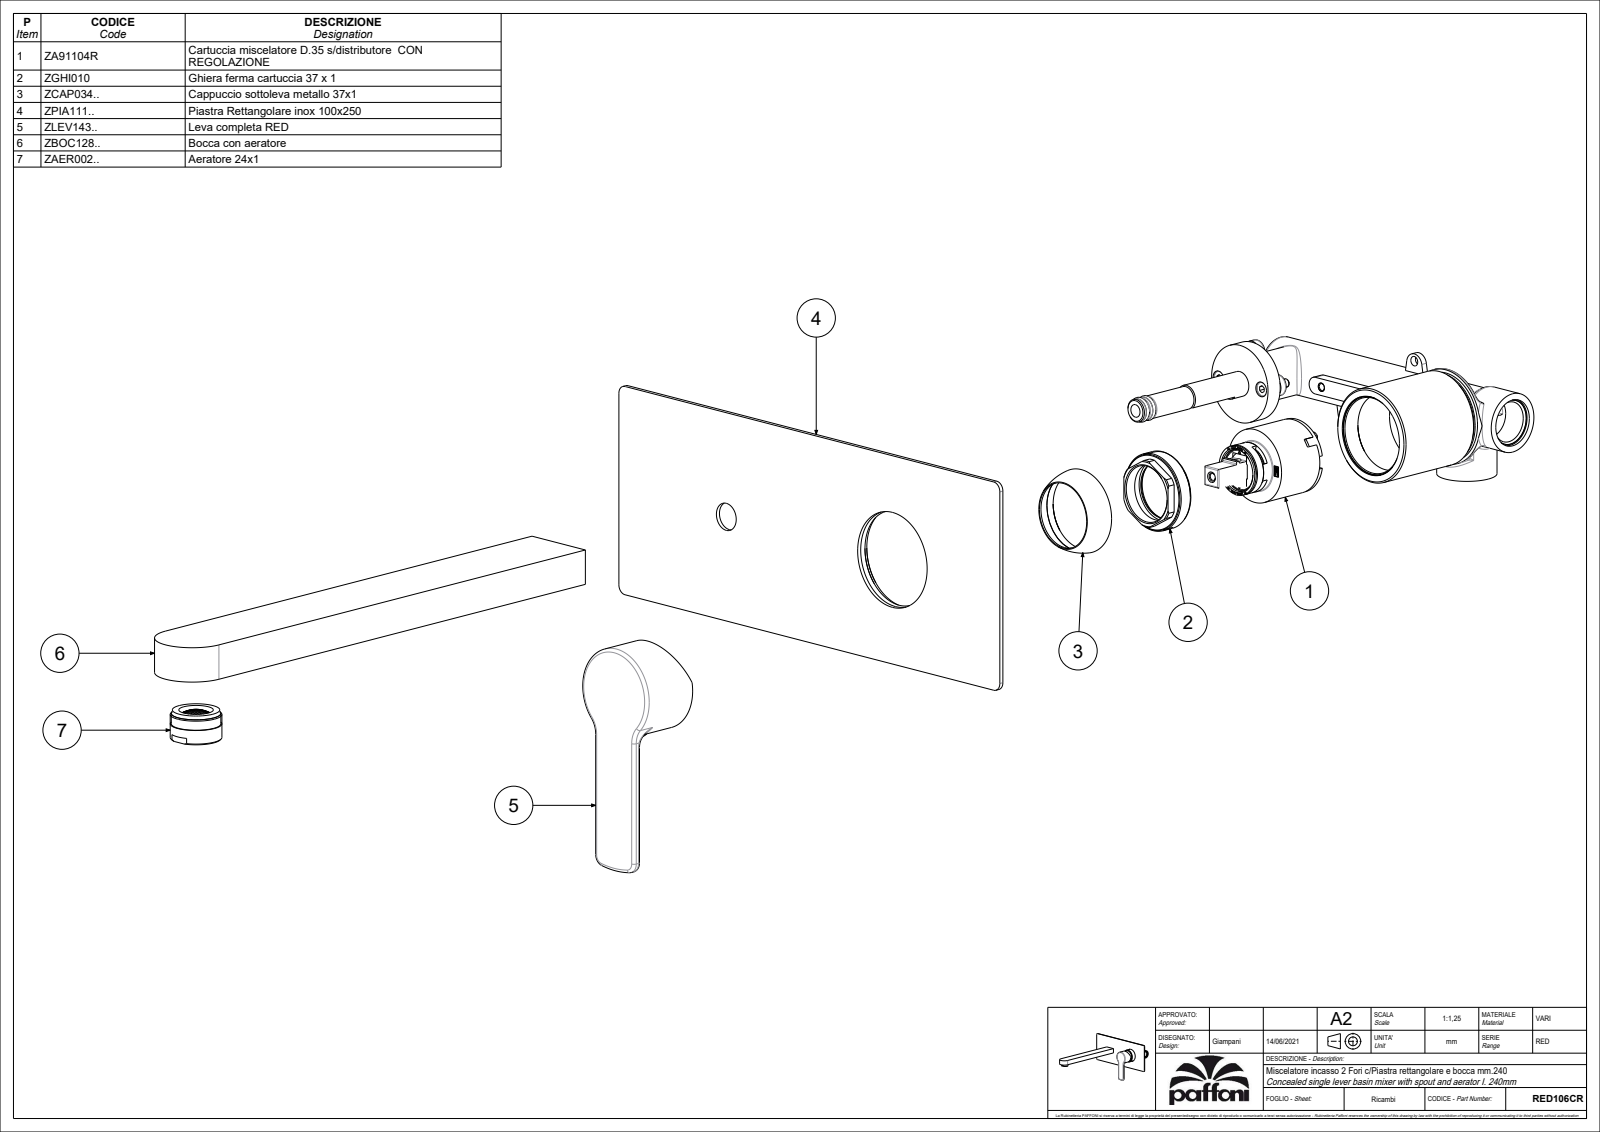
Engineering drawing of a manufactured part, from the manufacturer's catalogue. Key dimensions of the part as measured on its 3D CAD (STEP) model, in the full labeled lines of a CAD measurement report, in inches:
Part name (STEP PRODUCT): RED106CR
STEP written by: CREO PARAMETRIC BY PTC INC, 2020044 (CONFIG_CONTROL_DESIGN)
Units: inches
Bodies: 4 solids, 2520 faces (2011 planar, 283 cylindrical, 226 other)
Overall size (bounding box): 10.236 × 9.843 × 5.315
Volume: 13.41 in³ · Surface area: 191.6 in²
Round holes (diameter × count): ⌀0.13 ×2, ⌀0.157 ×2, ⌀0.236 ×2, ⌀0.118 ×1, ⌀0.177 ×1, ⌀0.197 ×1, ⌀0.433 ×1, ⌀0.472 ×1, ⌀0.512 ×1, ⌀0.591 ×1, ⌀0.63 ×1, ⌀0.669 ×1
Round bosses / shafts (diameter × count): ⌀1.764 ×1, ⌀1.693 ×1, ⌀1.378 ×1, ⌀0.945 ×1, ⌀0.925 ×1, ⌀0.921 ×1, ⌀0.858 ×1, ⌀0.768 ×1
Partial cylindrical surfaces — rounded edges, fillets, slot ends (radius × count): R0.02 ×45, R0.006 ×11, R0.012 ×4, R0.059 ×4, R0.157 ×4, R0.039 ×2, R0.083 ×2, R0.098 ×2
Main face-to-face distances: 0.079, 0.65, 1.378, 1.972, 1.894, 0.177, 2.15, 2.071, 1.644, 2.293
Hole centre spacings: 0.098, 0.492, 4.291, 4.293, 9.016, 9.452
